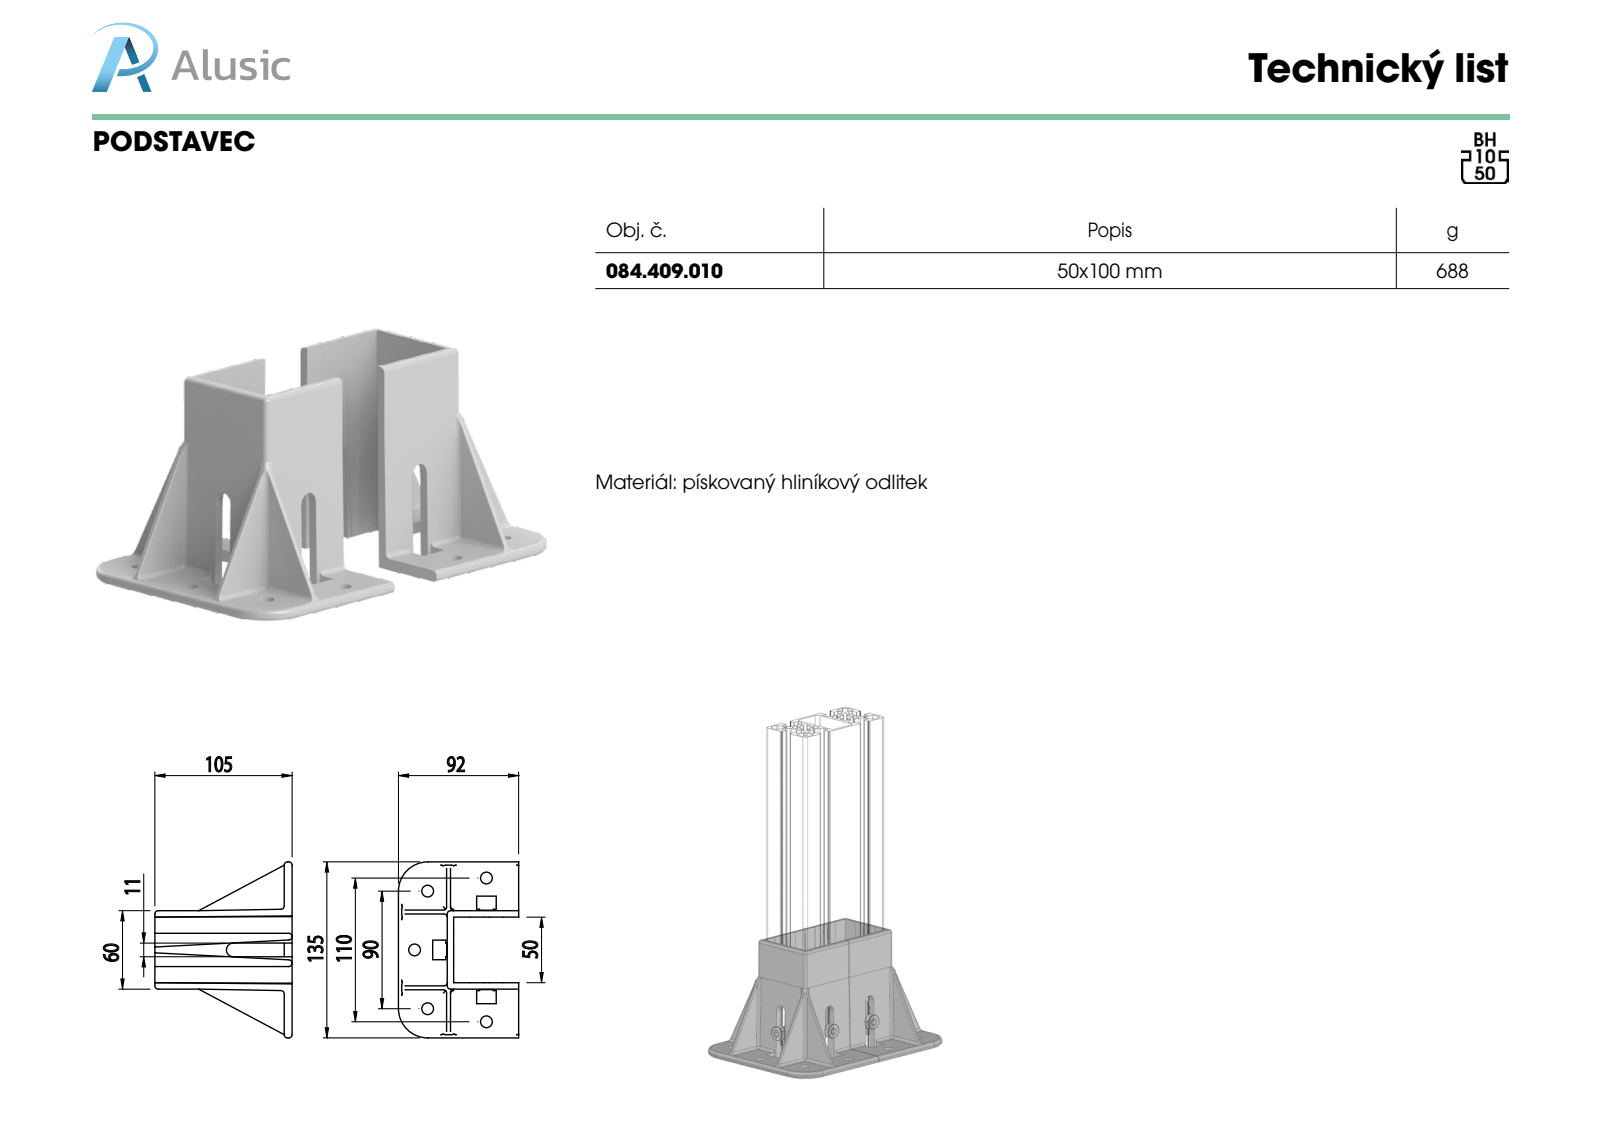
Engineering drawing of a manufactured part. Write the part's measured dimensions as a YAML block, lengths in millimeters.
part_name: "084.409.010"
step_written_by: "SolidWorks 2012 (CONFIG_CONTROL_DESIGN)"
units: millimeters
bodies: {solids: 1, faces: 189, planar: 84, cylindrical: 70, other: 35}
overall_size: [134.7, 105, 92]
volume: 128984
surface_area: 62186
round_holes:
  - {diameter: 9, count: 5}
partial_cylinders:
  - {radius: 2.5, count: 33}
  - {radius: 1, count: 9}
  - {radius: 5.25, count: 2}
  - {radius: 22.5, count: 2}
face_to_face_distances: [6, 3, 2.5, 0.5, 57.5, 60.5, 58, 60, 52.15, 54.65]
hole_center_spacings: [46.1, 77.78, 109.66, 90, 110]
